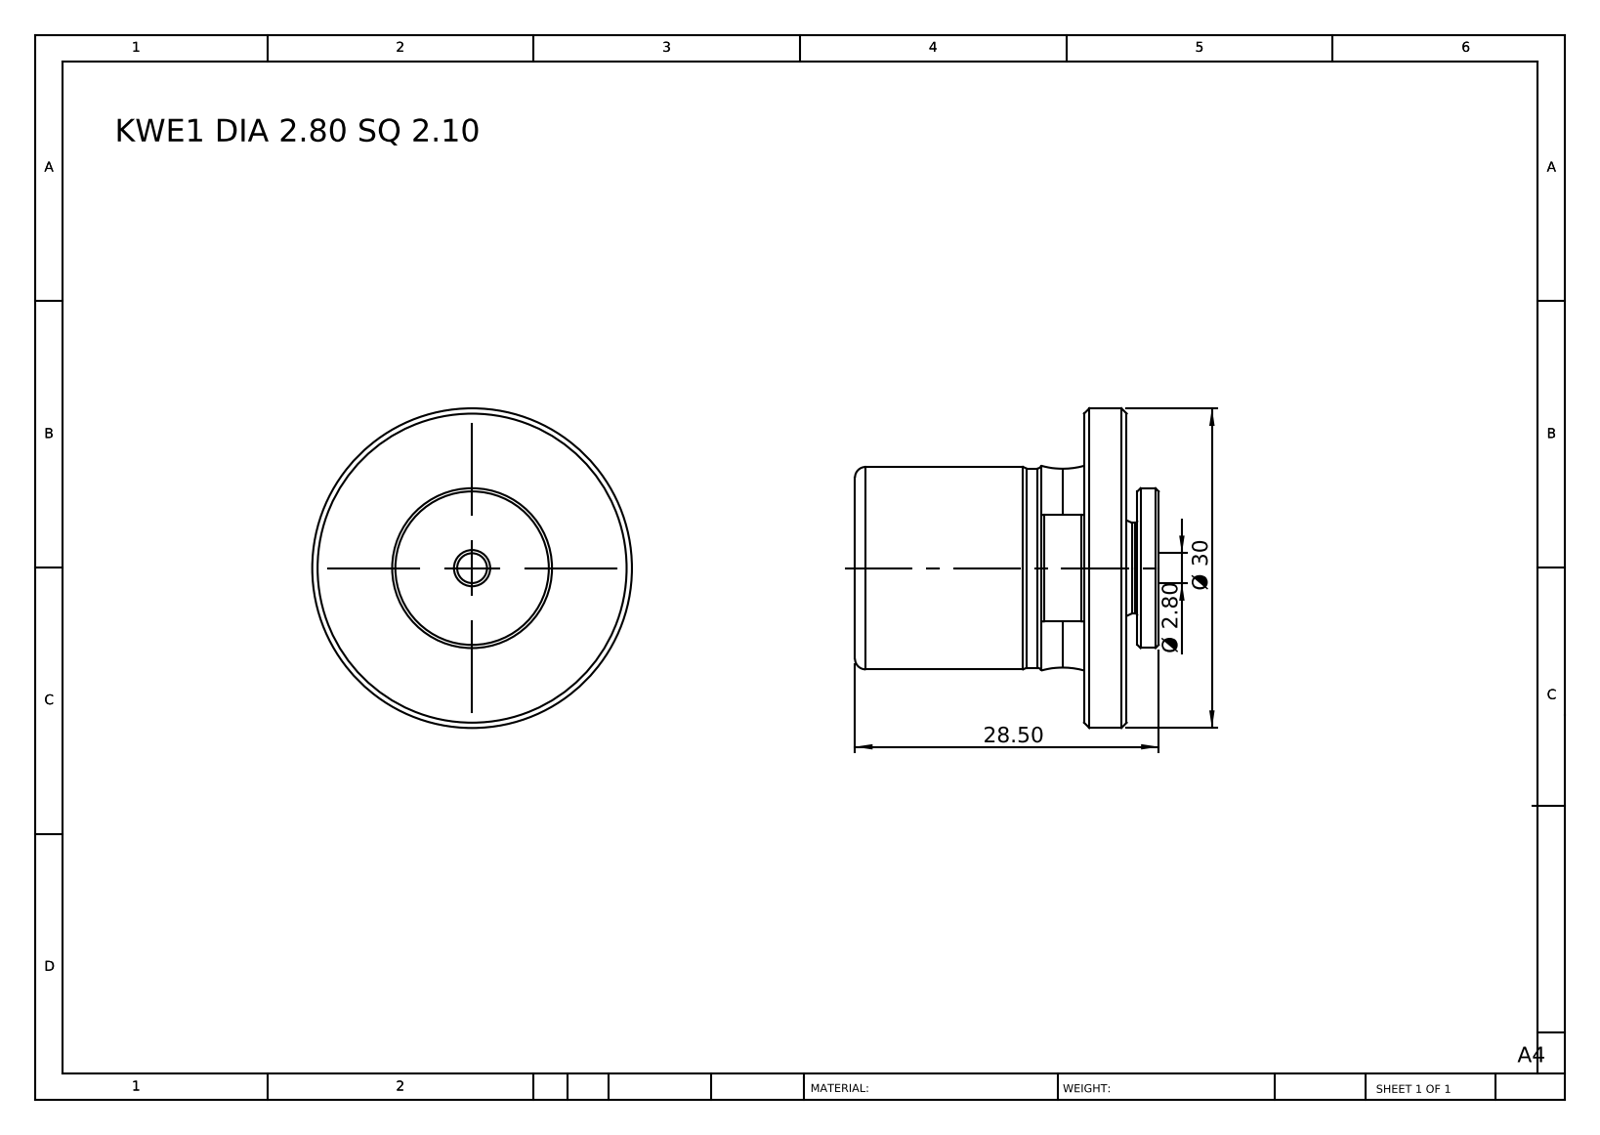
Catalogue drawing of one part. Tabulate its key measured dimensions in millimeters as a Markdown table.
| quantity | value |
| --- | --- |
| part name | KWE1 DIA 2.80 SQ 2.10 |
| STEP written by | SolidWorks 2014 (CONFIG_CONTROL_DESIGN) |
| units | millimeters |
| bodies | 1 solid, 56 faces (12 planar, 14 cylindrical, 30 other) |
| overall size | 30 × 30 × 28.5 |
| volume | 9 448 mm³ |
| surface area | 3 473 mm² |
| round holes (diameter × count) | 2.8 × 1 |
| round bosses / shafts (diameter × count) | 30 × 1, 19 × 1, 18.7 × 1, 15 × 1, 8.5 × 1 |
| partial cylindrical surfaces (radius × count) | 12.4 × 1 |
| main face-to-face distances | 4, 21.5, 25.5, 3, 7, 28.5, 1, 26.5, 5, 2 |
